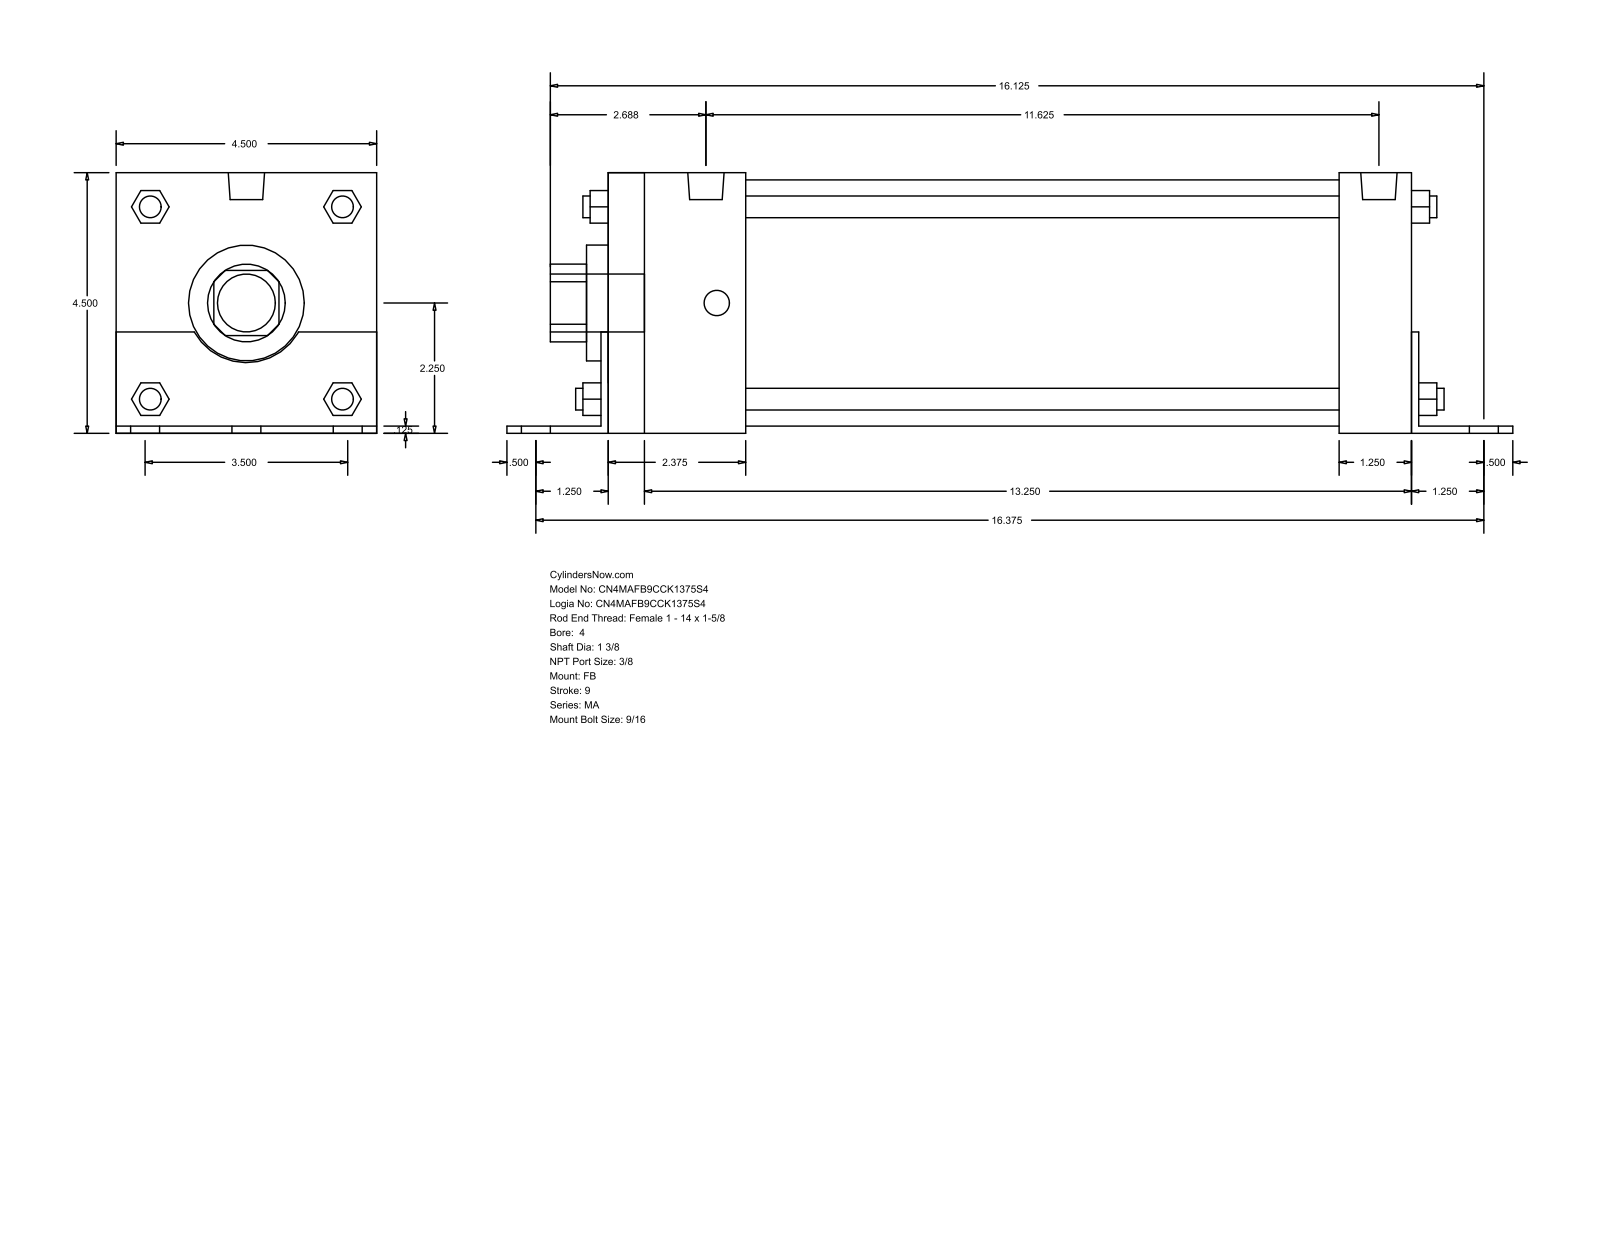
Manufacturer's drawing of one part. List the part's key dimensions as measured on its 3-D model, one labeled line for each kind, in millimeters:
Part name (STEP PRODUCT): MA_FB__0400_1.375
STEP written by: GSSL Pune (CONFIG_CONTROL_DESIGN)
Units: millimetres
Bodies: 0 solids, 140 faces (105 planar, 35 cylindrical, 0 other)
Overall size (bounding box): 441.32 × 114.35 × 114.3
Round holes (diameter × count): ⌀34.92 ×1, ⌀50.8 ×1, ⌀107.95 ×1
Round bosses / shafts (diameter × count): ⌀14.29 ×6, ⌀11.11 ×4, ⌀9.53 ×4, ⌀15.93 ×2, ⌀25.4 ×1
Partial cylindrical surfaces — rounded edges, fillets, slot ends (radius × count): R17.06 ×1, R26.16 ×1
Main face-to-face distances: 114.3, 3.17, 114.35, 3.12, 111.18, 352.42, 3.18, 355.6, 34.93, 60.32
